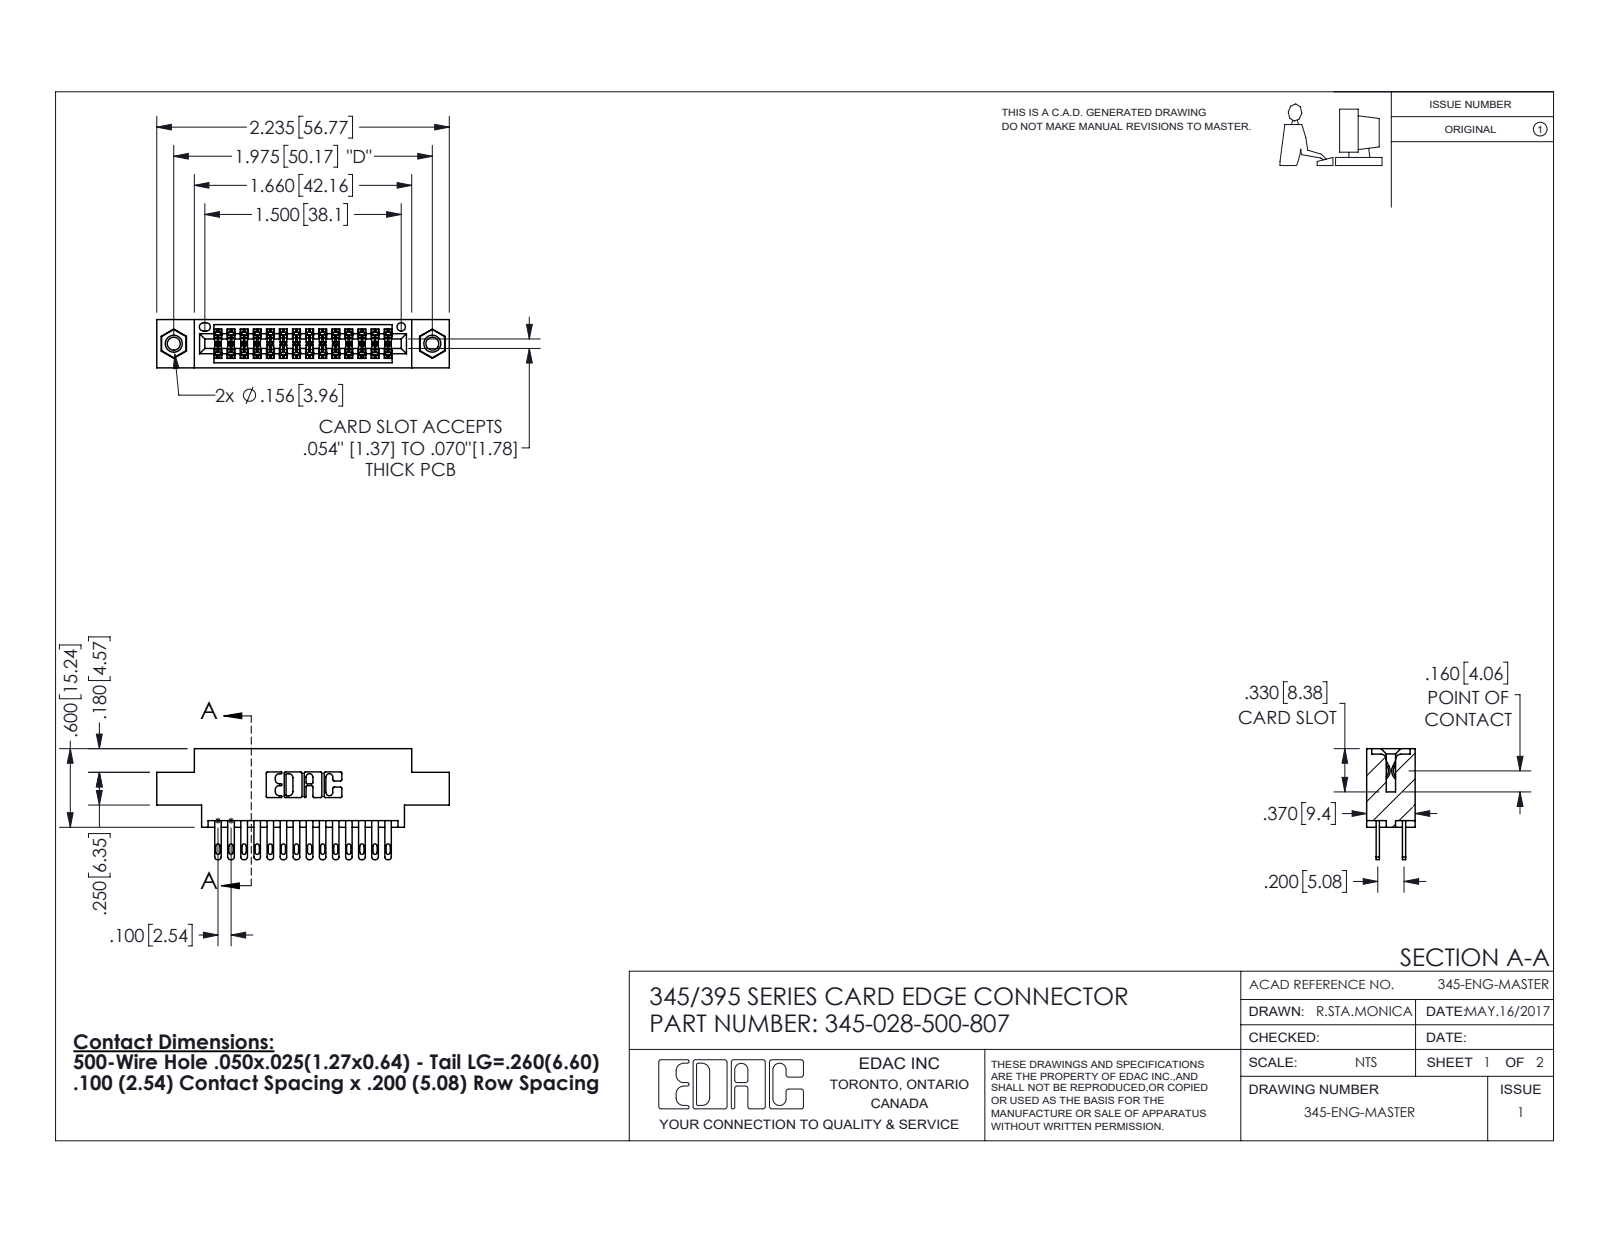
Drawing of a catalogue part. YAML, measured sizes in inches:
part_name: "345 Part_0.170 Offset - 0.156 Dia-TI; 345-028-500-807; 345-250-001_345-250-005-103; 345-292-001_345-293-100"
step_written_by: "SolidWorks 2016 (CONFIG_CONTROL_DESIGN)"
units: inches
bodies: {solids: 31, faces: 1478, planar: 872, cylindrical: 590, other: 16}
overall_size: [2.235, 0.847, 0.37]
volume: 0.318
surface_area: 11.81
round_holes:
  - {diameter: 0.098, count: 2}
  - {diameter: 0.125, count: 2}
  - {diameter: 0.156, count: 2}
  - {diameter: 0.064, count: 1}
round_bosses_or_shafts:
  - {diameter: 0.155, count: 2}
partial_cylinders:
  - {radius: 0.006, count: 42}
  - {radius: 0.016, count: 28}
  - {radius: 0.02, count: 28}
  - {radius: 0.01, count: 22}
  - {radius: 0.007, count: 6}
  - {radius: 0.031, count: 6}
  - {radius: 0.026, count: 3}
  - {radius: 0.014, count: 2}
face_to_face_distances: [0.072, 0.298, 0.2, 0.37, 0.098, 0.272, 0.025, 0.225, 0.175, 0.1]
hole_center_spacings: [0.27, 1.742, 1.975]
